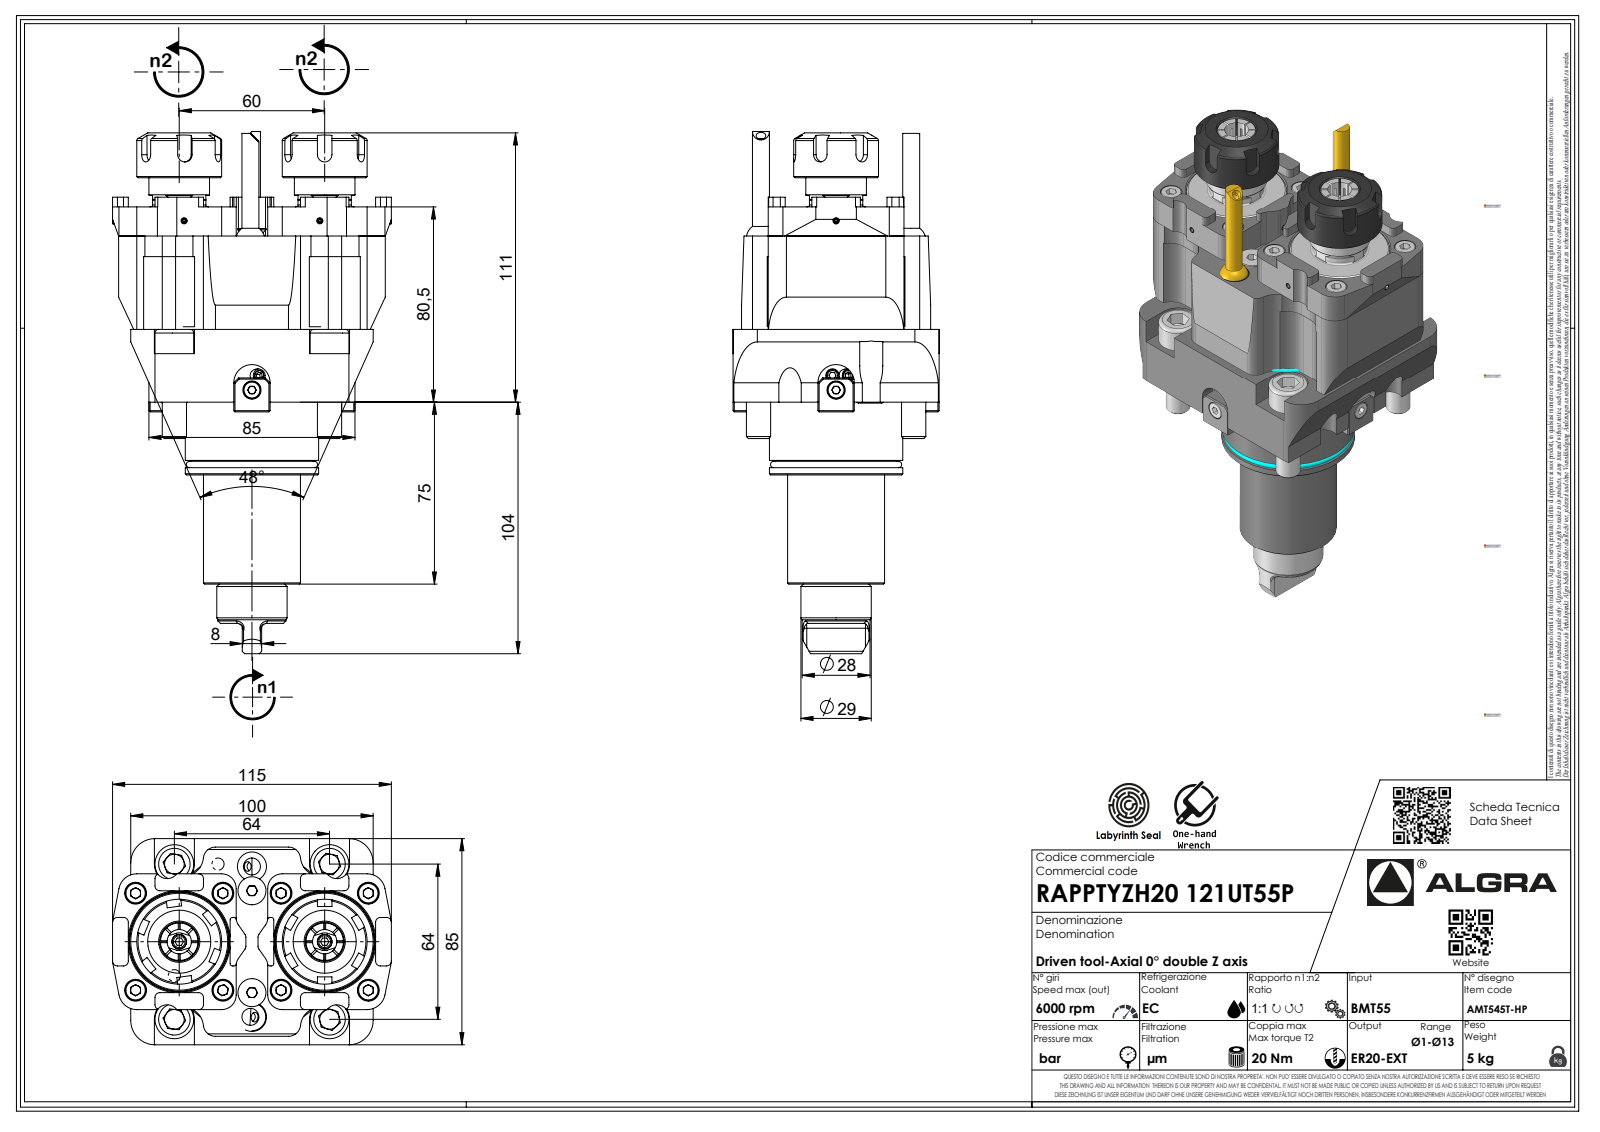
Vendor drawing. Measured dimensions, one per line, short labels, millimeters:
name: RAPPTYH20121UT55P
written by: SolidWorks 2016 (AUTOMOTIVE_DESIGN)
unit: mm
bodies: 1 solid, 886 faces (590 planar, 166 cylindrical, 130 other)
size: 215.28 × 115 × 85
volume: 741 682 mm³; area: 78 839 mm²
holes: 2× ⌀4, 1× ⌀2.1
bosses: 4× ⌀16, 4× ⌀10, 2× ⌀35, 2× ⌀25, 2× ⌀7, 1× ⌀55, 1× ⌀50.2, 1× ⌀40
rounds: 32× R2, 20× R5, 12× R8.25, 9× R3, 8× R1, 8× R8.2, 8× R10, 7× R0.33
face distances: 80.5, 85, 30, 15, 38.5, 12, 12.5, 60, 70, 68.5
